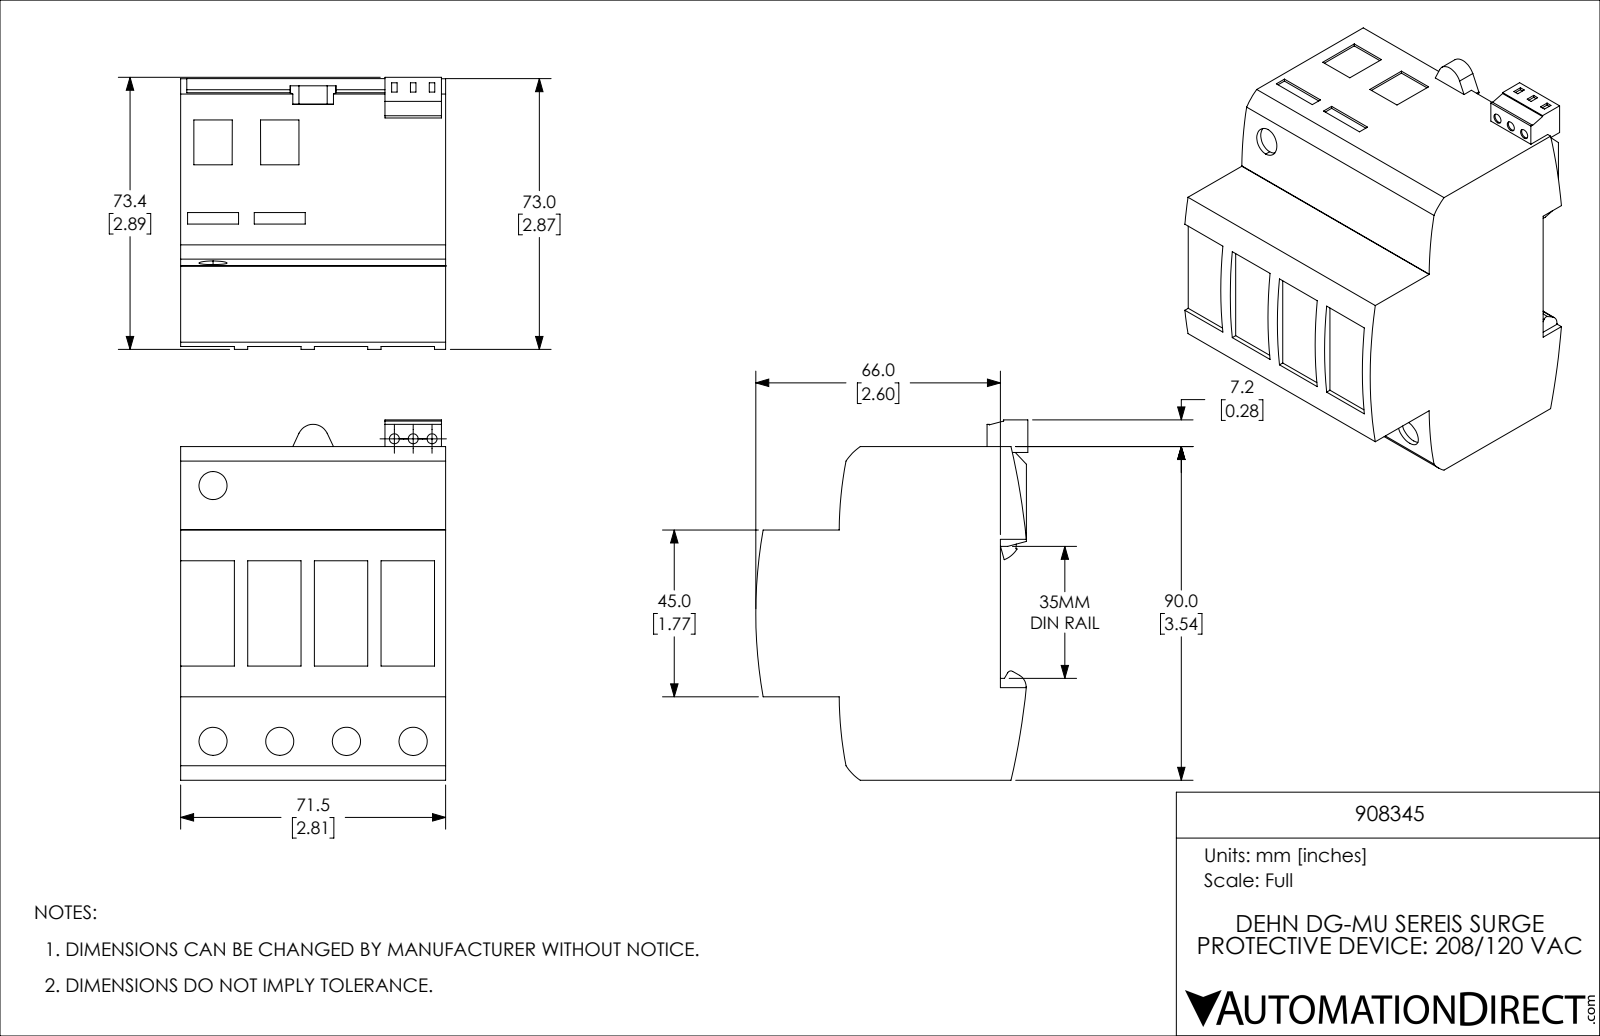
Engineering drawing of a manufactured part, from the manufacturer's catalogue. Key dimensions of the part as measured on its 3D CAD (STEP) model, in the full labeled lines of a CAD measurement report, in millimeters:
Part name (STEP PRODUCT): 908345
STEP written by: SolidWorks 2019 (CONFIG_CONTROL_DESIGN)
Units: millimetres
Bodies: 1 solid, 178 faces (142 planar, 25 cylindrical, 11 other)
Overall size (bounding box): 97.2 × 73.4 × 71.5
Volume: 367 400 mm³ · Surface area: 35 050 mm²
Round holes (diameter × count): ⌀2.7 ×3
Partial cylindrical surfaces — rounded edges, fillets, slot ends (radius × count): R2 ×2, R100 ×2, R1 ×1, R3.5 ×1, R4.2 ×1, R14 ×1, R14 ×1, R98.5 ×1
Main face-to-face distances: 71.5, 22.5, 67.5, 90, 64, 45, 7, 71, 66.9, 0.7
Hole centre spacings: 5.1, 5.1, 10.2
